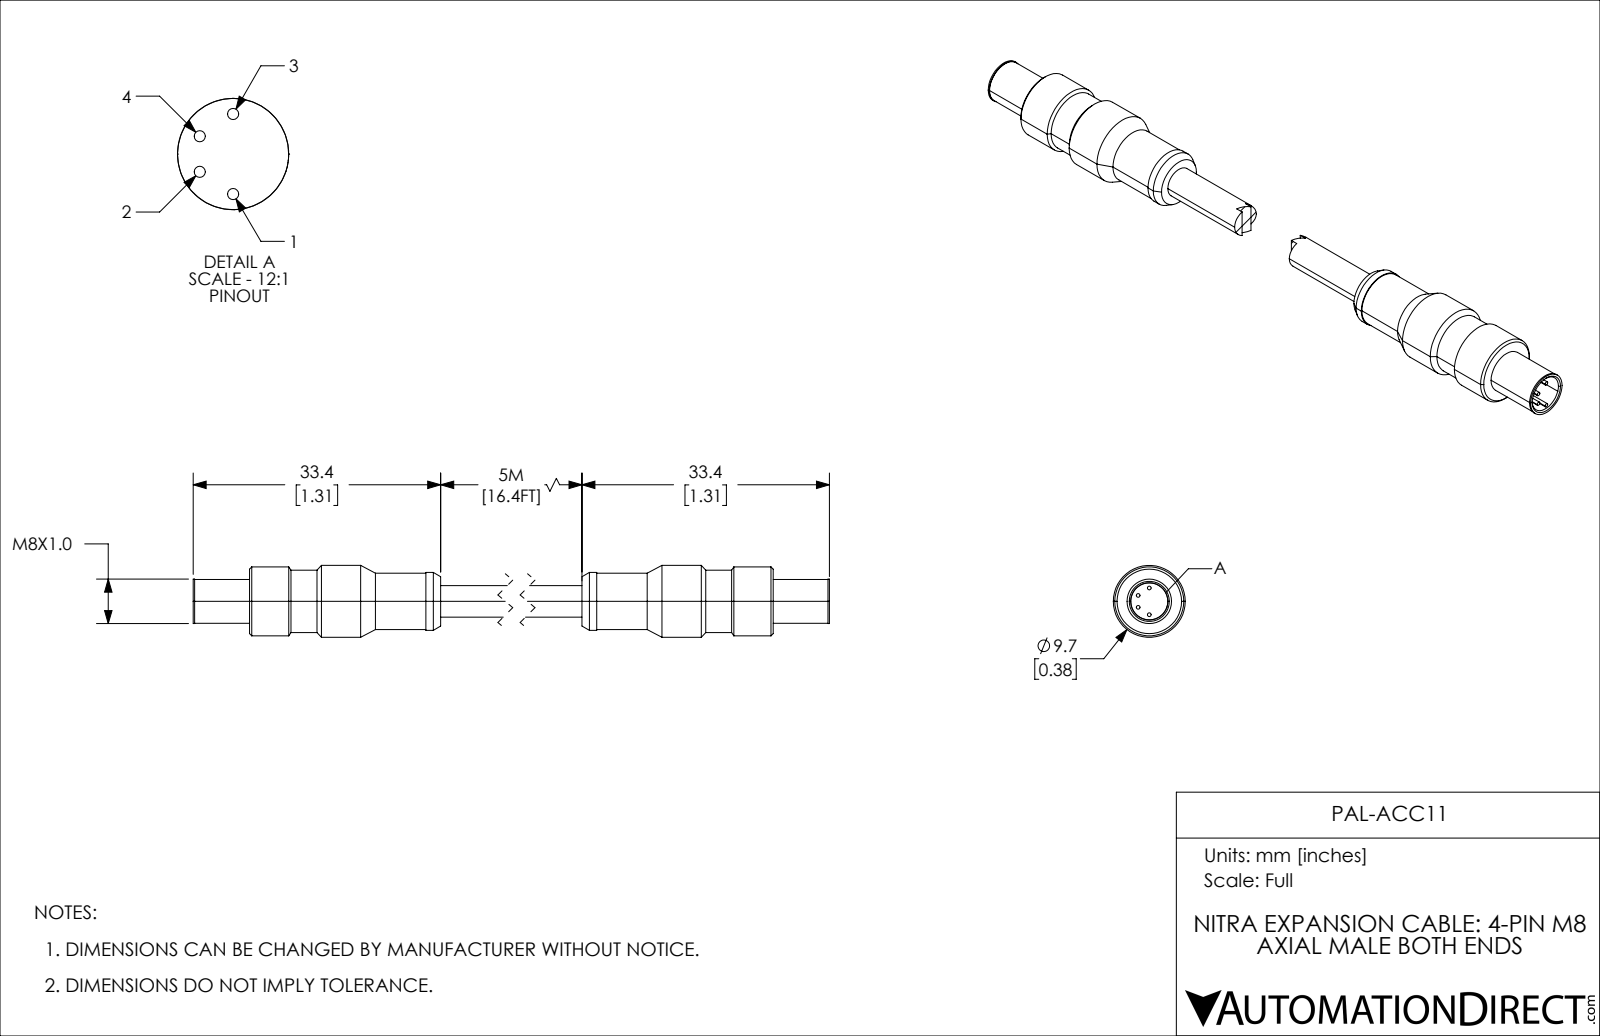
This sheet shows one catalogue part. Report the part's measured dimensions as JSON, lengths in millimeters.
{"part_name": "PAL-ACC11", "step_written_by": "SolidWorks 2019 (CONFIG_CONTROL_DESIGN)", "units": "millimeters", "bodies": {"solids": 1, "faces": 99, "planar": 20, "cylindrical": 52, "other": 27}, "overall_size": [62.62, 23.89, 9.7], "volume_mm3": 4144, "surface_area_mm2": 2952, "round_holes": [[5, 2]], "round_bosses_or_shafts": [[0.5, 8], [9.7, 2], [9.3, 2], [8.4, 2], [7.8, 2], [7.6, 2], [6, 2], [5.9, 2]], "face_to_face_distances": [25.8, 2.6, 28.4, 5, 7.6, 33.4, 31.4, 26.4, 23.8, 2], "hole_center_spacings": [14.19]}
